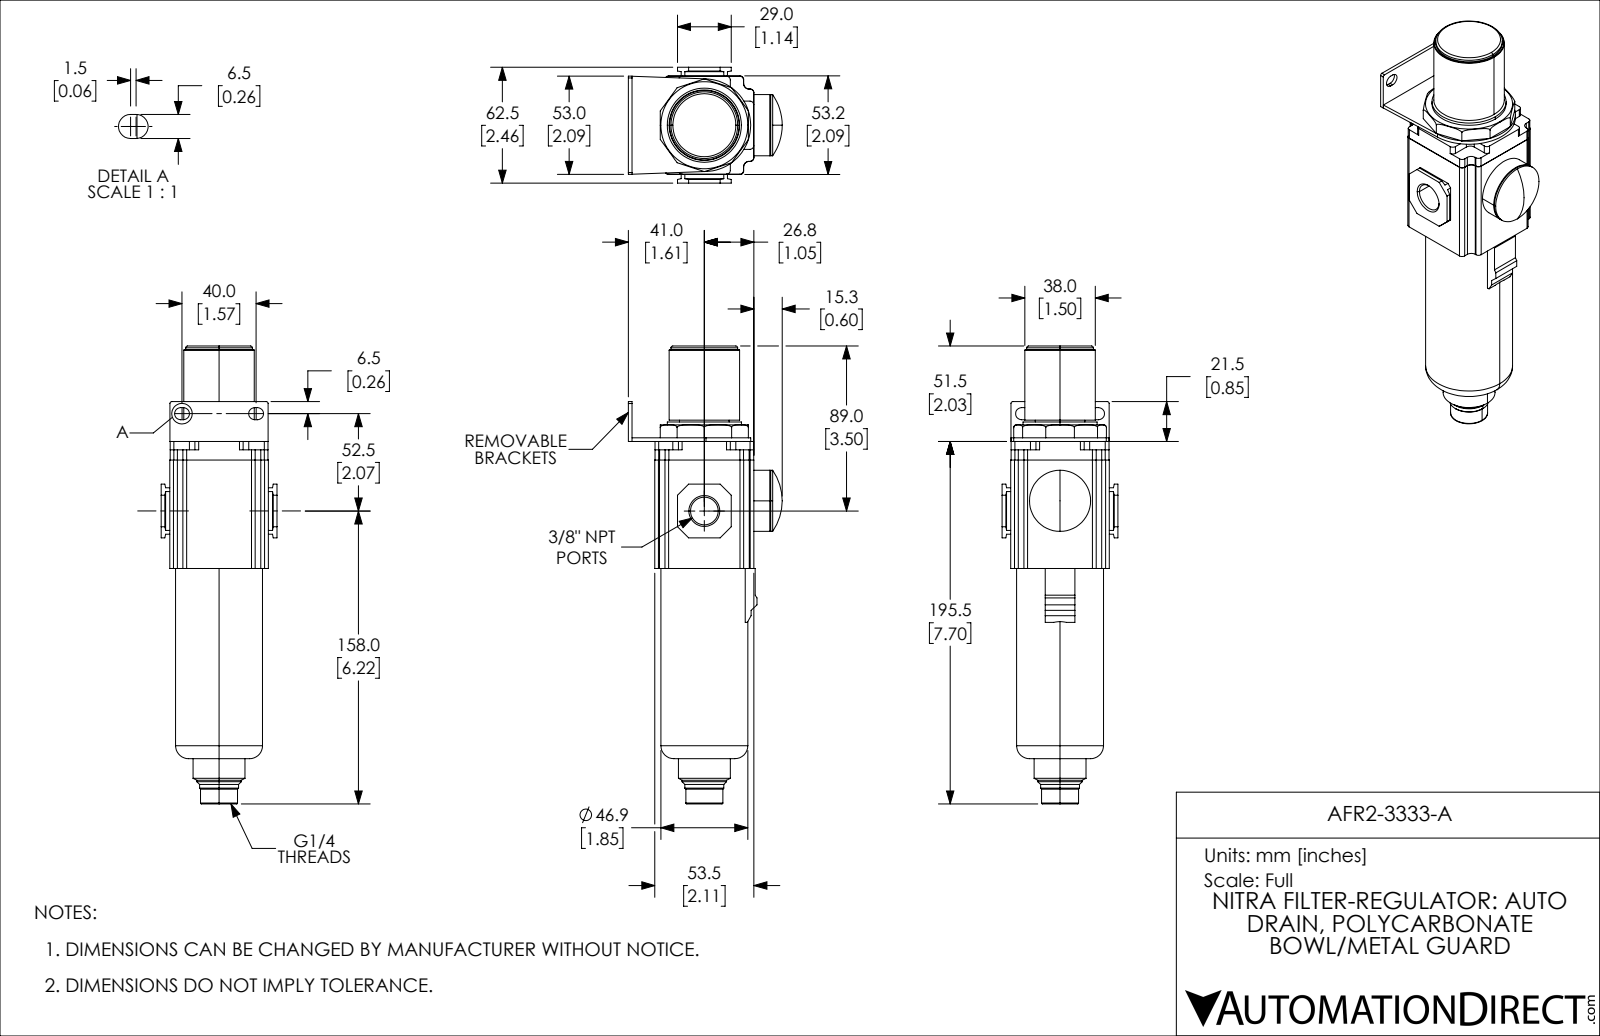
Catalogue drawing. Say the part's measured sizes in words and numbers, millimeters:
The part is named "AFR2-3333-A". Its 3-D file was written by "SolidWorks 2019 (CONFIG_CONTROL_DESIGN)". It is 1 solid with 221 faces: 124 planar, 71 cylindrical and 26 other. Overall it measures 247 by 83.03 by 62.5 millimeters. Its volume is 449 570 cubic millimeters and its surface area 52 239 square millimeters. Round holes: 1 of diameter 11.45, 1 of diameter 14.95. Round bosses or shafts: 1 of diameter 46.9, 1 of diameter 40, 1 of diameter 38, 1 of diameter 36, 1 of diameter 33, 1 of diameter 28, 1 of diameter 26.78, 1 of diameter 24. Partial cylindrical surfaces (rounded edges, fillets, slot ends): 24 of radius 2, 12 of radius 3, 4 of radius 3.25, 2 of radius 1, 1 of radius 25. The main face-to-face distances are 2, 53.2, 53.5, 14.25, 4.65, 57.85, 12.25, 67.75, 51.5, 49.5.
